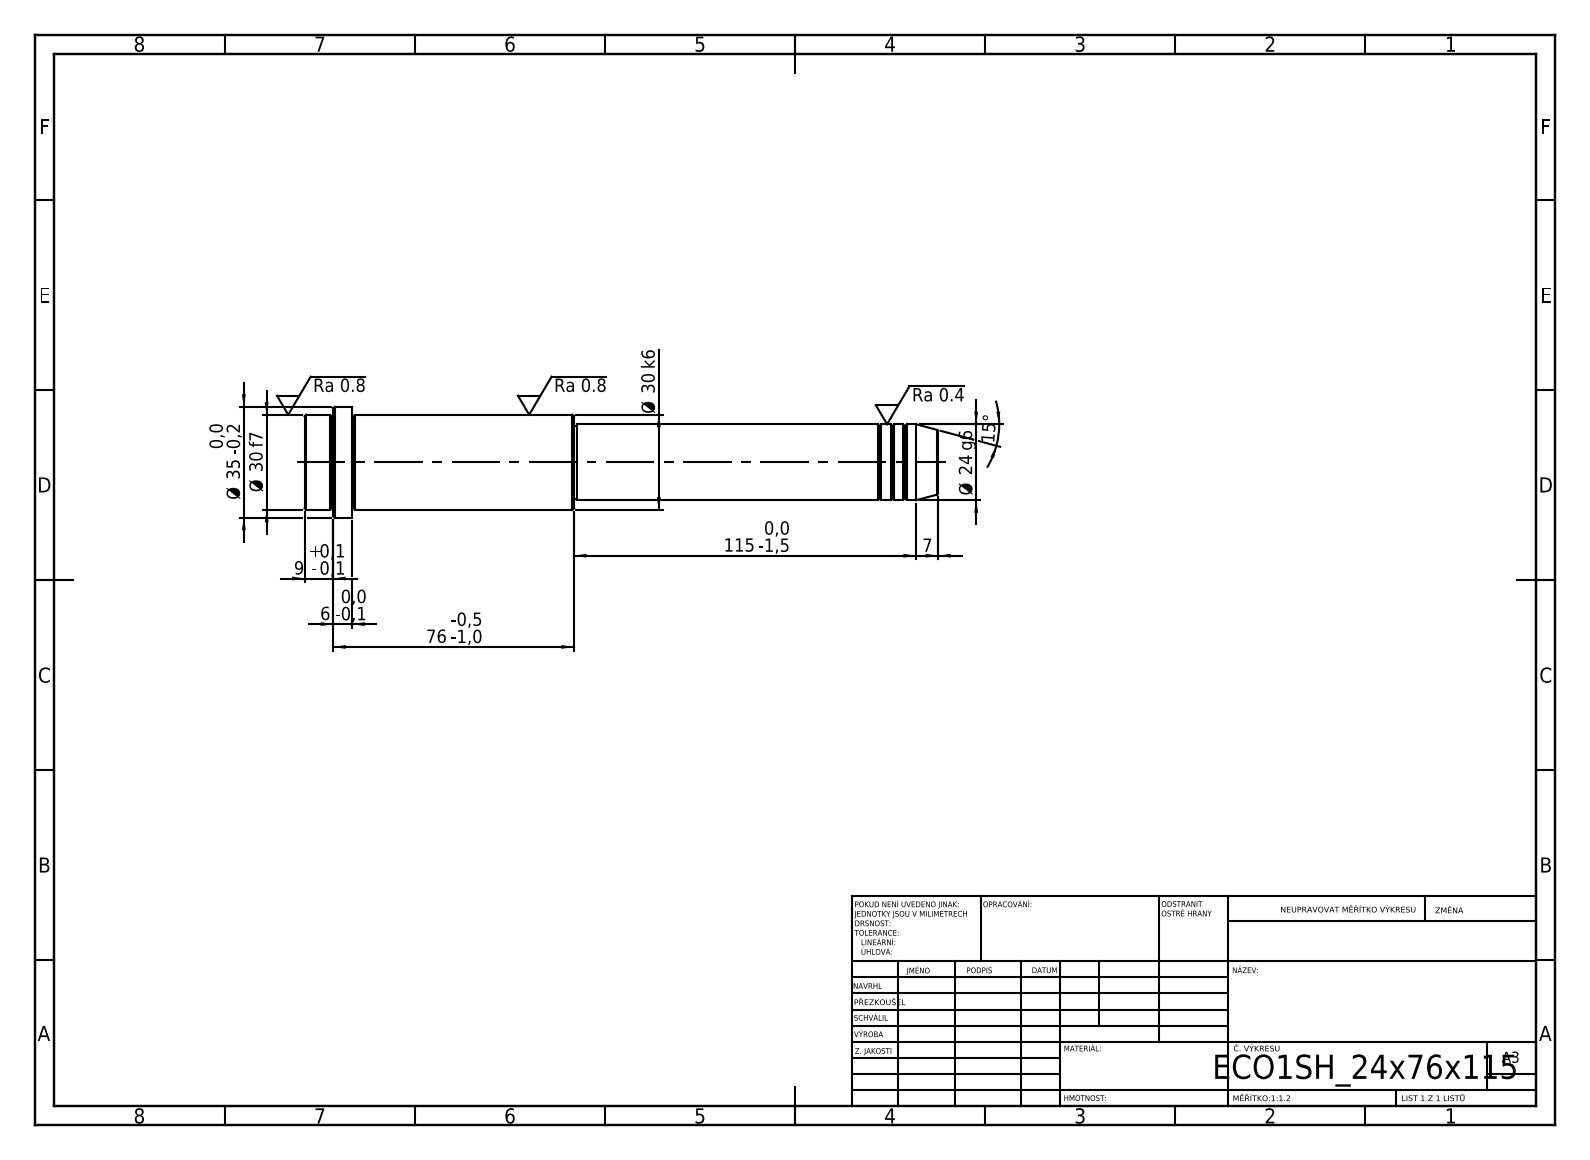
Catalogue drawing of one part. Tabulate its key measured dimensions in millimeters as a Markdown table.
| quantity | value |
| --- | --- |
| STEP written by | SolidWorks 2019 (CONFIG_CONTROL_DESIGN) |
| units | millimeters |
| bodies | 1 solid, 52 faces (6 planar, 16 cylindrical, 30 other) |
| overall size | 200 × 35 × 35 |
| volume | 112 934 mm³ |
| surface area | 18 742 mm² |
| round bosses / shafts (diameter × count) | 35 × 1, 30 × 1, 24 × 1, 23 × 1 |
| main face-to-face distances | 200, 185, 15, 115, 70, 85, 191, 76, 6, 9 |
